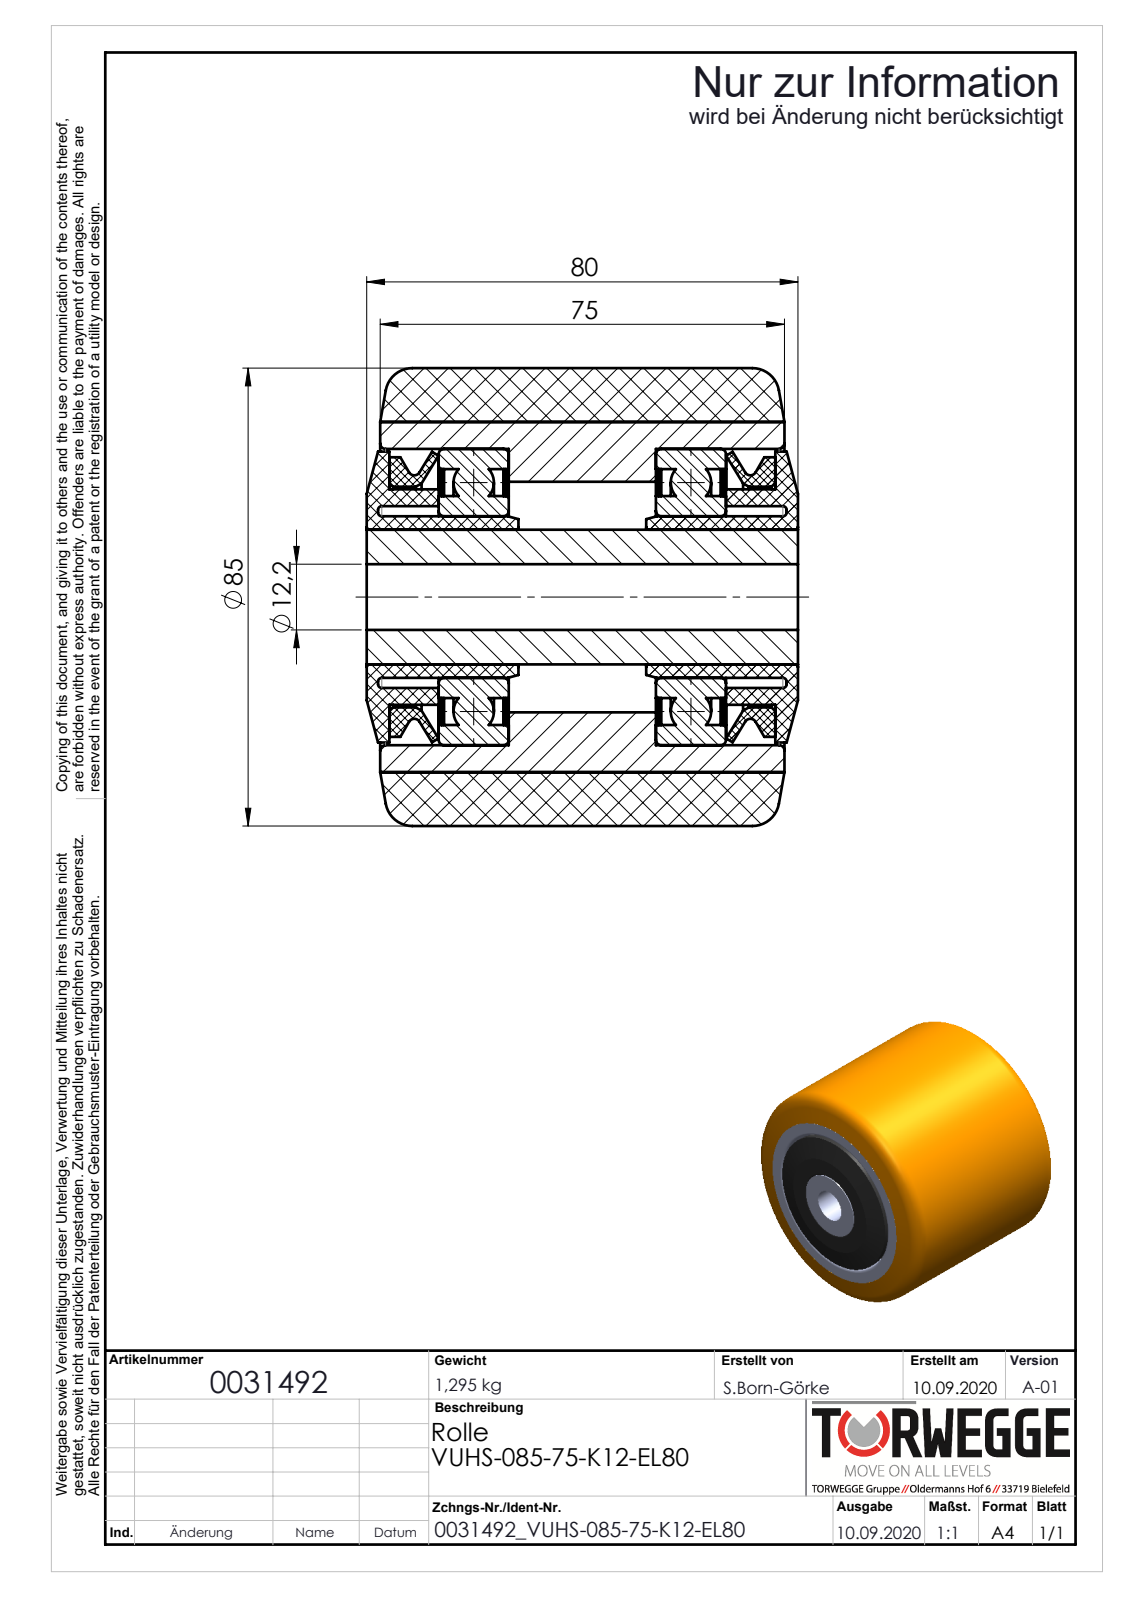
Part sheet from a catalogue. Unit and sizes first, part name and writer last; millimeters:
Units: millimetres
Overall size (bounding box): 85 × 85 × 80
Round holes (diameter × count): ⌀12.2 ×1, ⌀25 ×1, ⌀30 ×1, ⌀33.75 ×1, ⌀37.5 ×1, ⌀40.98 ×1, ⌀42.8 ×1, ⌀47.5 ×1, ⌀55 ×1, ⌀65 ×1
Round bosses / shafts (diameter × count): ⌀85 ×1, ⌀54 ×1, ⌀51.9 ×1, ⌀40 ×1
Main face-to-face distances: 0.5, 40.3, 12, 22.15, 49.45, 1, 12.5, 11.5, 40.8, 39.8
Volume: 370 281 mm³ · Surface area: 133 398 mm²
Bodies: 13 solids, 210 faces (34 planar, 84 cylindrical, 92 other)
Part name (STEP PRODUCT): 0031492
STEP written by: SolidWorks 2018 (AUTOMOTIVE_DESIGN)
